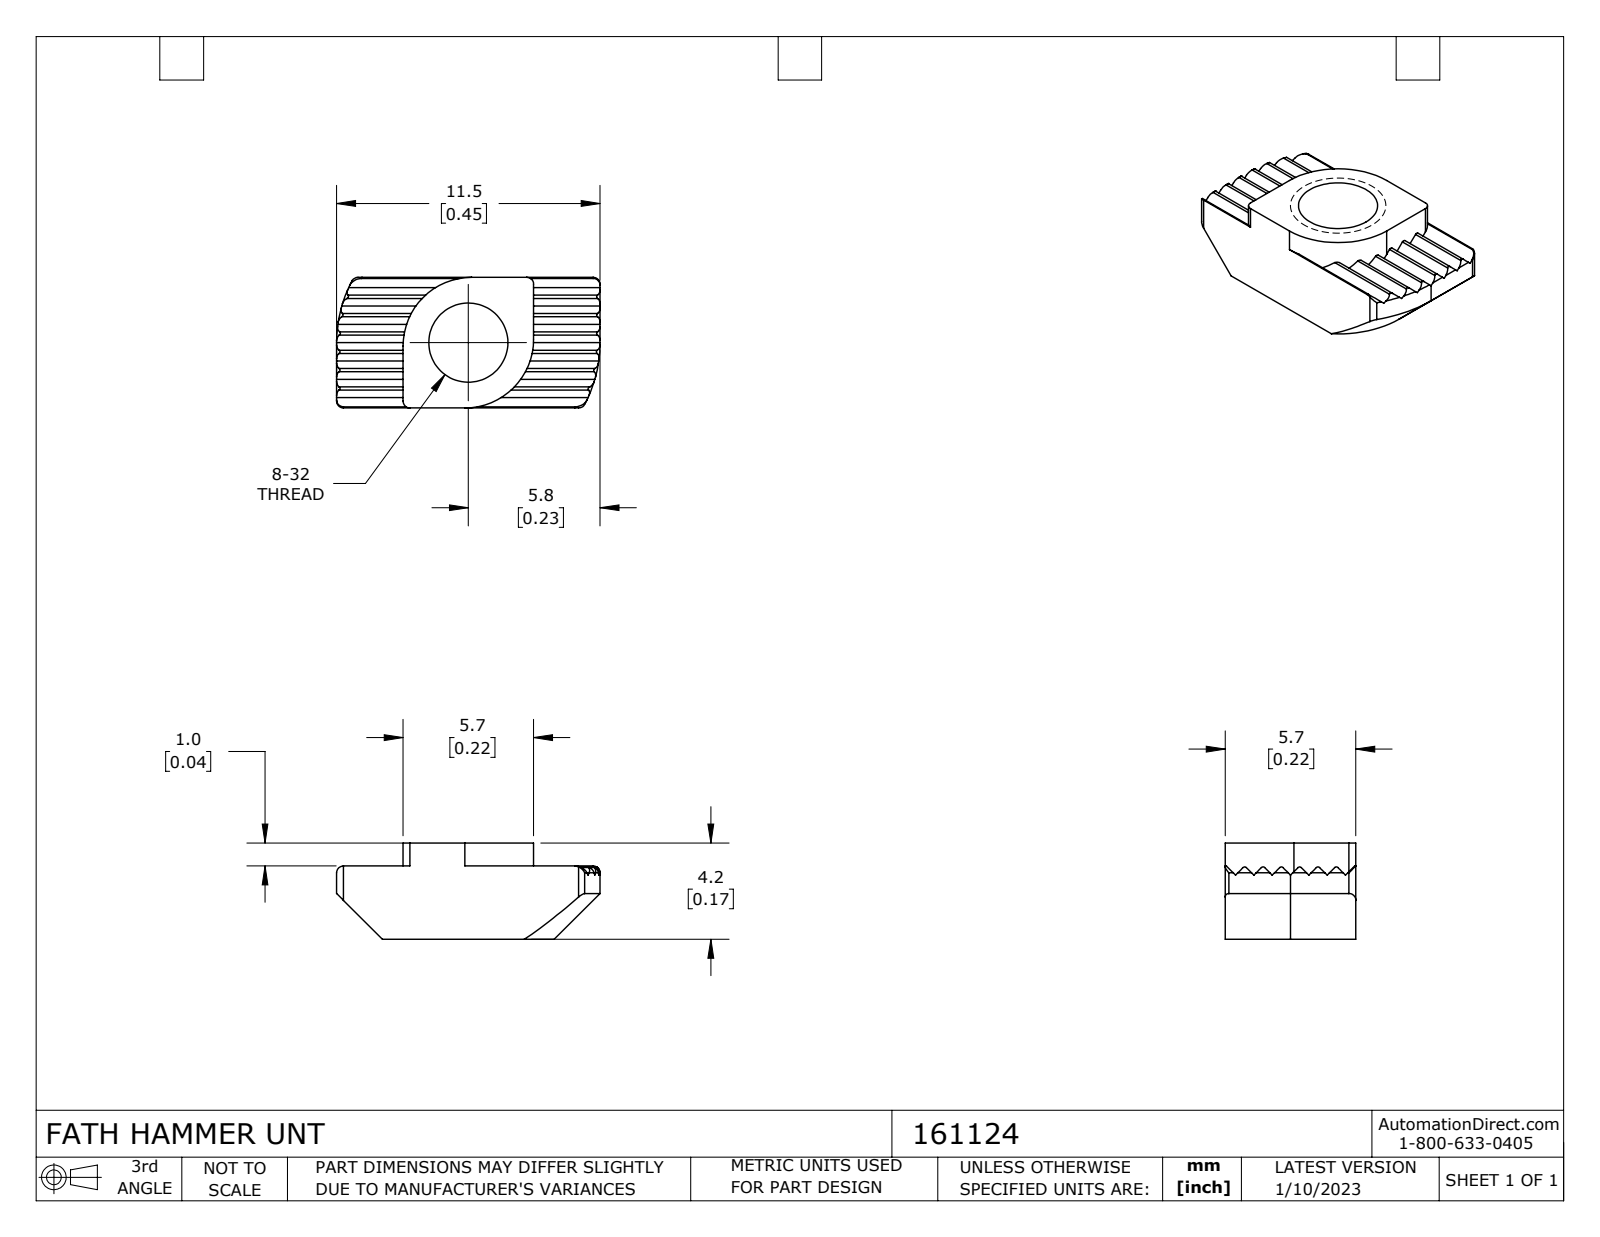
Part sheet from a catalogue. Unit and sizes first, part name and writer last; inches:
Units: inches
Overall size (bounding box): 0.453 × 0.224 × 0.165
Round holes (diameter × count): ⌀0.136 ×1
Partial cylindrical surfaces — rounded edges, fillets, slot ends (radius × count): R0.012 ×8, R0.004 ×6, R0.118 ×2, R0.226 ×1
Main face-to-face distances: 0.224, 0.022, 0.044, 0.067, 0.165, 0.111, 0.089, 0.022, 0.134, 0.089
Volume: 0.01 in³ · Surface area: 0.42 in²
Bodies: 1 solid, 84 faces (42 planar, 32 cylindrical, 10 other)
Part name (STEP PRODUCT): 161124
STEP written by: SolidWorks 2021 (CONFIG_CONTROL_DESIGN)
